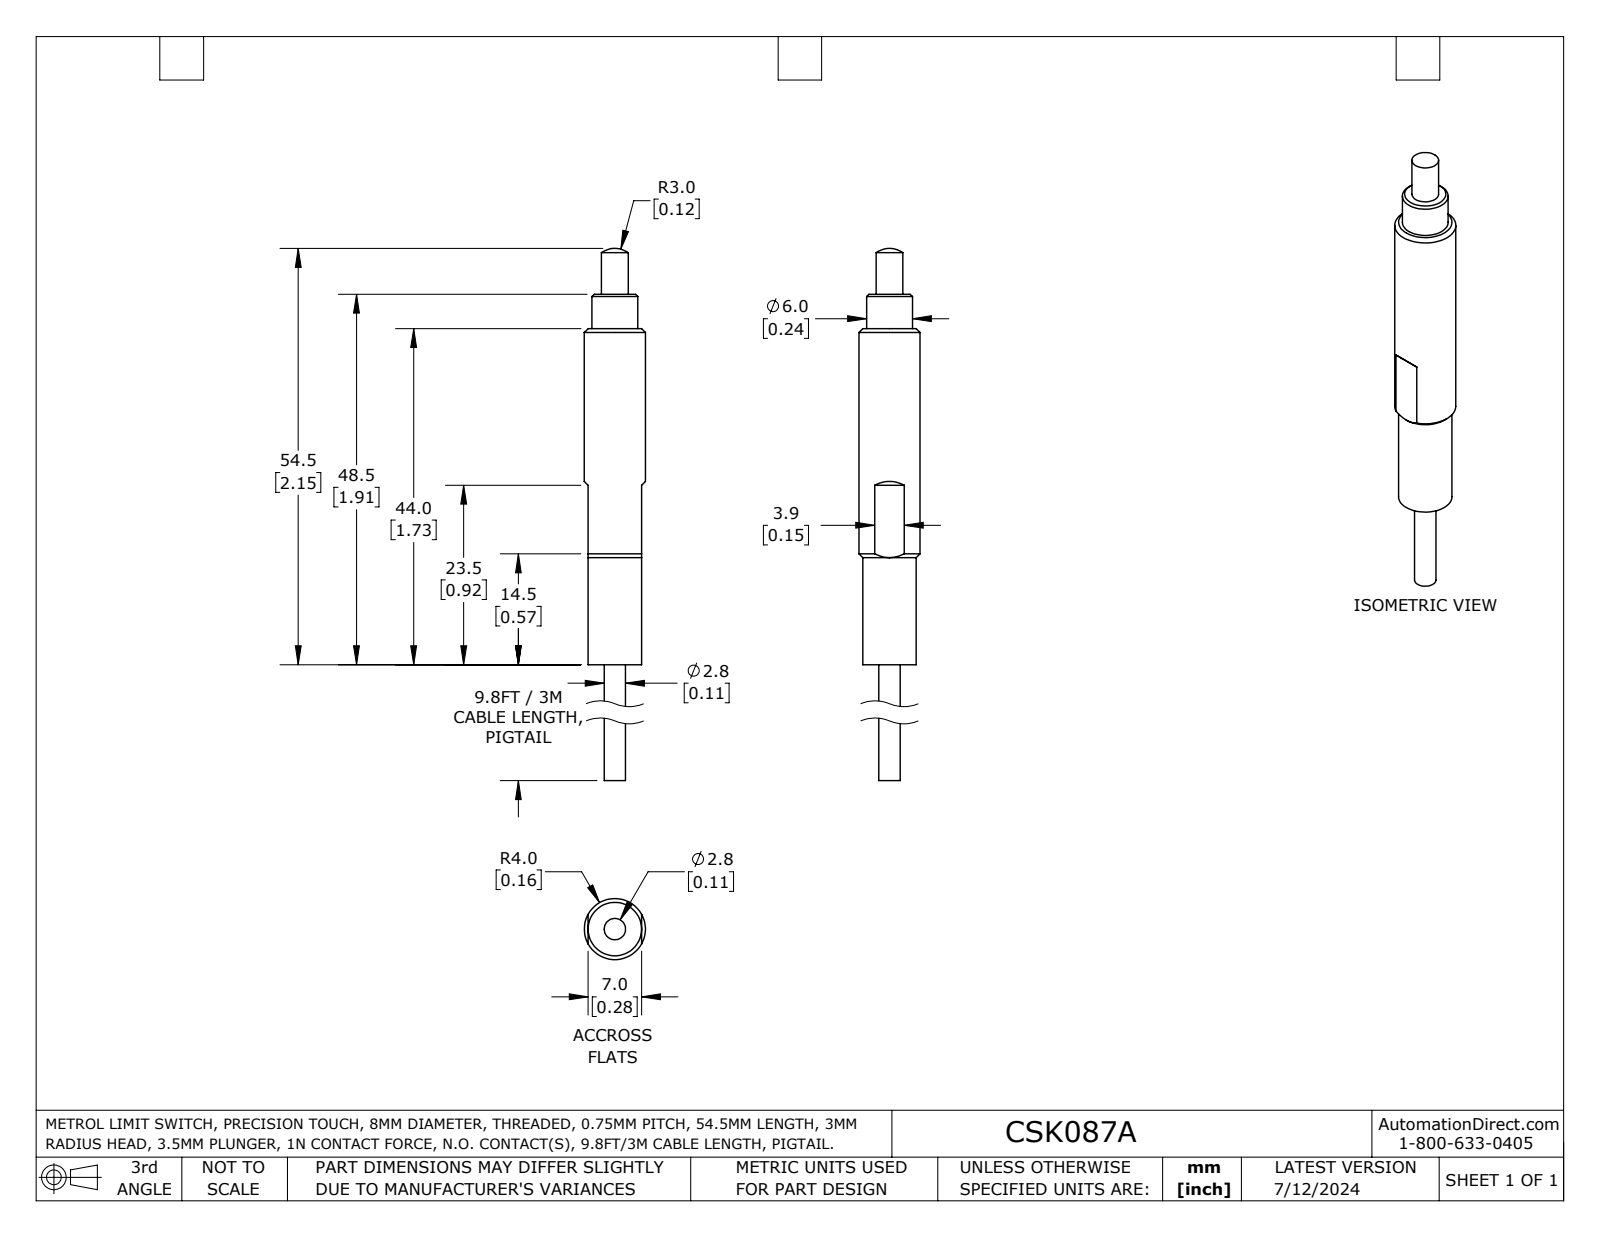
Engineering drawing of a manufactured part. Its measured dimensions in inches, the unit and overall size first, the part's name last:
Units: inches
Overall size (bounding box): 2.382 × 0.315 × 0.315
Round bosses / shafts (diameter × count): ⌀0.315 ×1, ⌀0.276 ×1, ⌀0.236 ×1, ⌀0.138 ×1, ⌀0.11 ×1
Main face-to-face distances: 0.276, 1.909, 1.732, 0.177, 0.236, 1.969, 2.146
Volume: 0.136 in³ · Surface area: 2.075 in²
Bodies: 1 solid, 18 faces (8 planar, 5 cylindrical, 5 other)
Part name (STEP PRODUCT): CSK087A
STEP written by: SolidWorks 2023 (AUTOMOTIVE_DESIGN)
